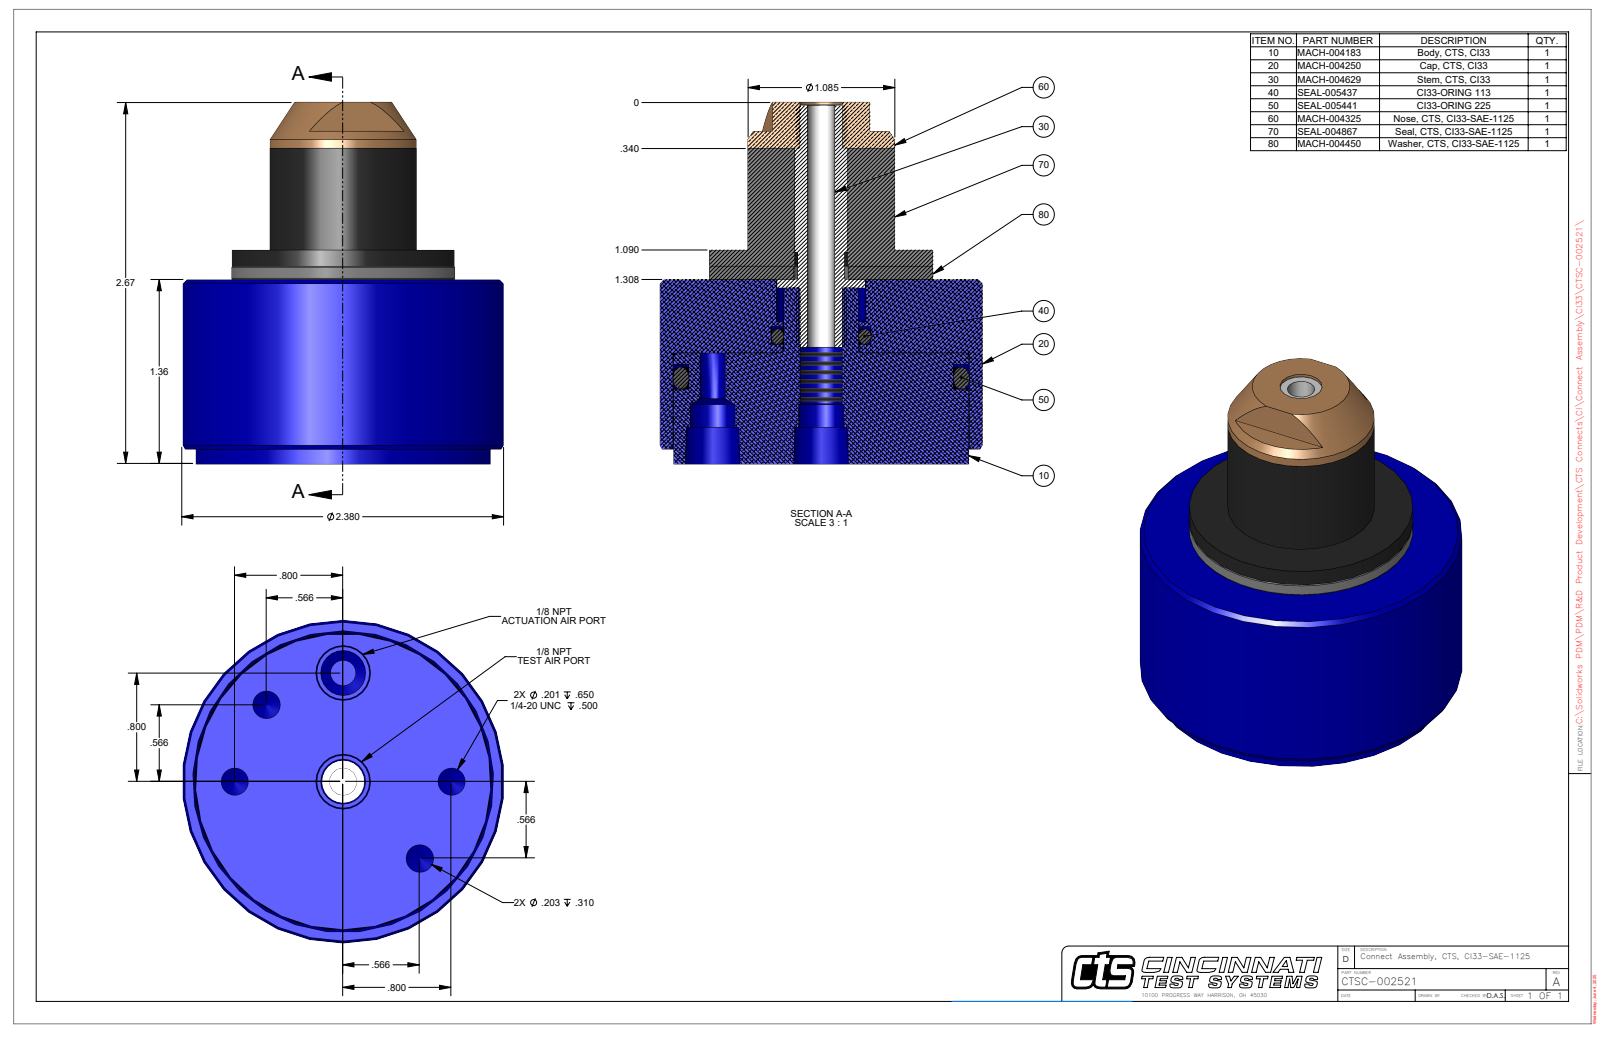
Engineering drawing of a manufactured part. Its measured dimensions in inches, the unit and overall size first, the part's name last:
Units: inches
Overall size (bounding box): 2.668 × 2.38 × 2.38
Round holes (diameter × count): ⌀0.201 ×2, ⌀0.203 ×2, ⌀0.332 ×2, ⌀0.203 ×1, ⌀0.313 ×1, ⌀2.188 ×1
Round bosses / shafts (diameter × count): ⌀2.38 ×1, ⌀2.178 ×1, ⌀1.65 ×1, ⌀1.085 ×1
Main face-to-face distances: 1.36, 1.578, 0.218, 0.11, 1.25, 1.468, 2.668, 2.558, 1.308, 1.09
Hole centre spacings: 0.8, 0.612, 1.478, 1.131, 1.6
Volume: 7.115 in³ · Surface area: 31.21 in²
Bodies: 1 solid, 70 faces (18 planar, 28 cylindrical, 24 other)
Part name (STEP PRODUCT): CTSC-002521
STEP written by: SolidWorks 2023 (AUTOMOTIVE_DESIGN)
